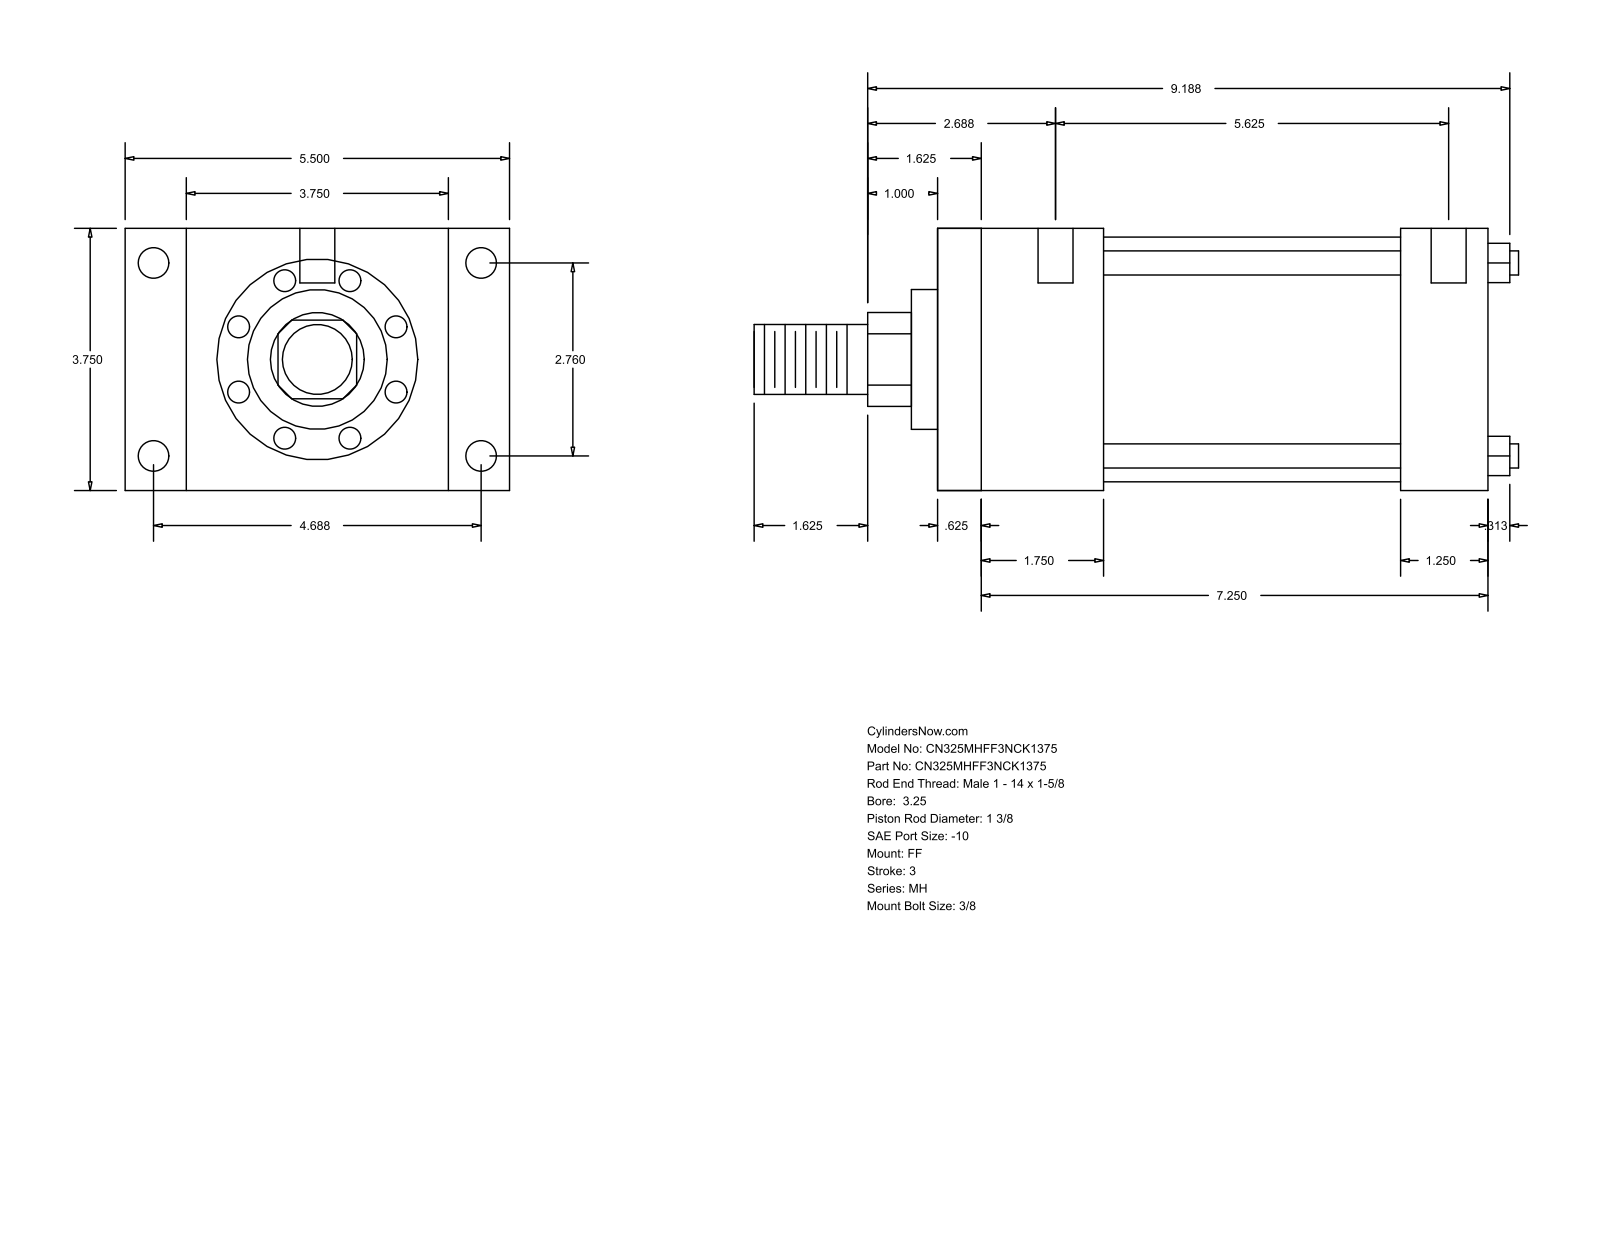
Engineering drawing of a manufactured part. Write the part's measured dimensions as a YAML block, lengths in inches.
part_name: "MH_FF__0325_1.375"
step_written_by: "GSSL Pune (CONFIG_CONTROL_DESIGN)"
units: inches
bodies: {solids: 0, faces: 92, planar: 64, cylindrical: 28, other: 0}
overall_size: [10.937, 5.5, 3.75]
round_holes:
  - {diameter: 0.219, count: 4}
  - {diameter: 0.438, count: 4}
  - {diameter: 0.5, count: 2}
round_bosses_or_shafts:
  - {diameter: 0.345, count: 4}
  - {diameter: 3.5, count: 1}
  - {diameter: 2, count: 1}
  - {diameter: 1.375, count: 1}
  - {diameter: 1, count: 1}
partial_cylinders:
  - {radius: 0.672, count: 1}
face_to_face_distances: [3.75, 7.875, 0.625, 7.25, 0.875, 4.625, 6.625, 6, 1.25, 2.375]
hole_center_spacings: [2.76, 4.687, 5.439, 5.875, 0.063, 0.187, 5.625, 5.688]
